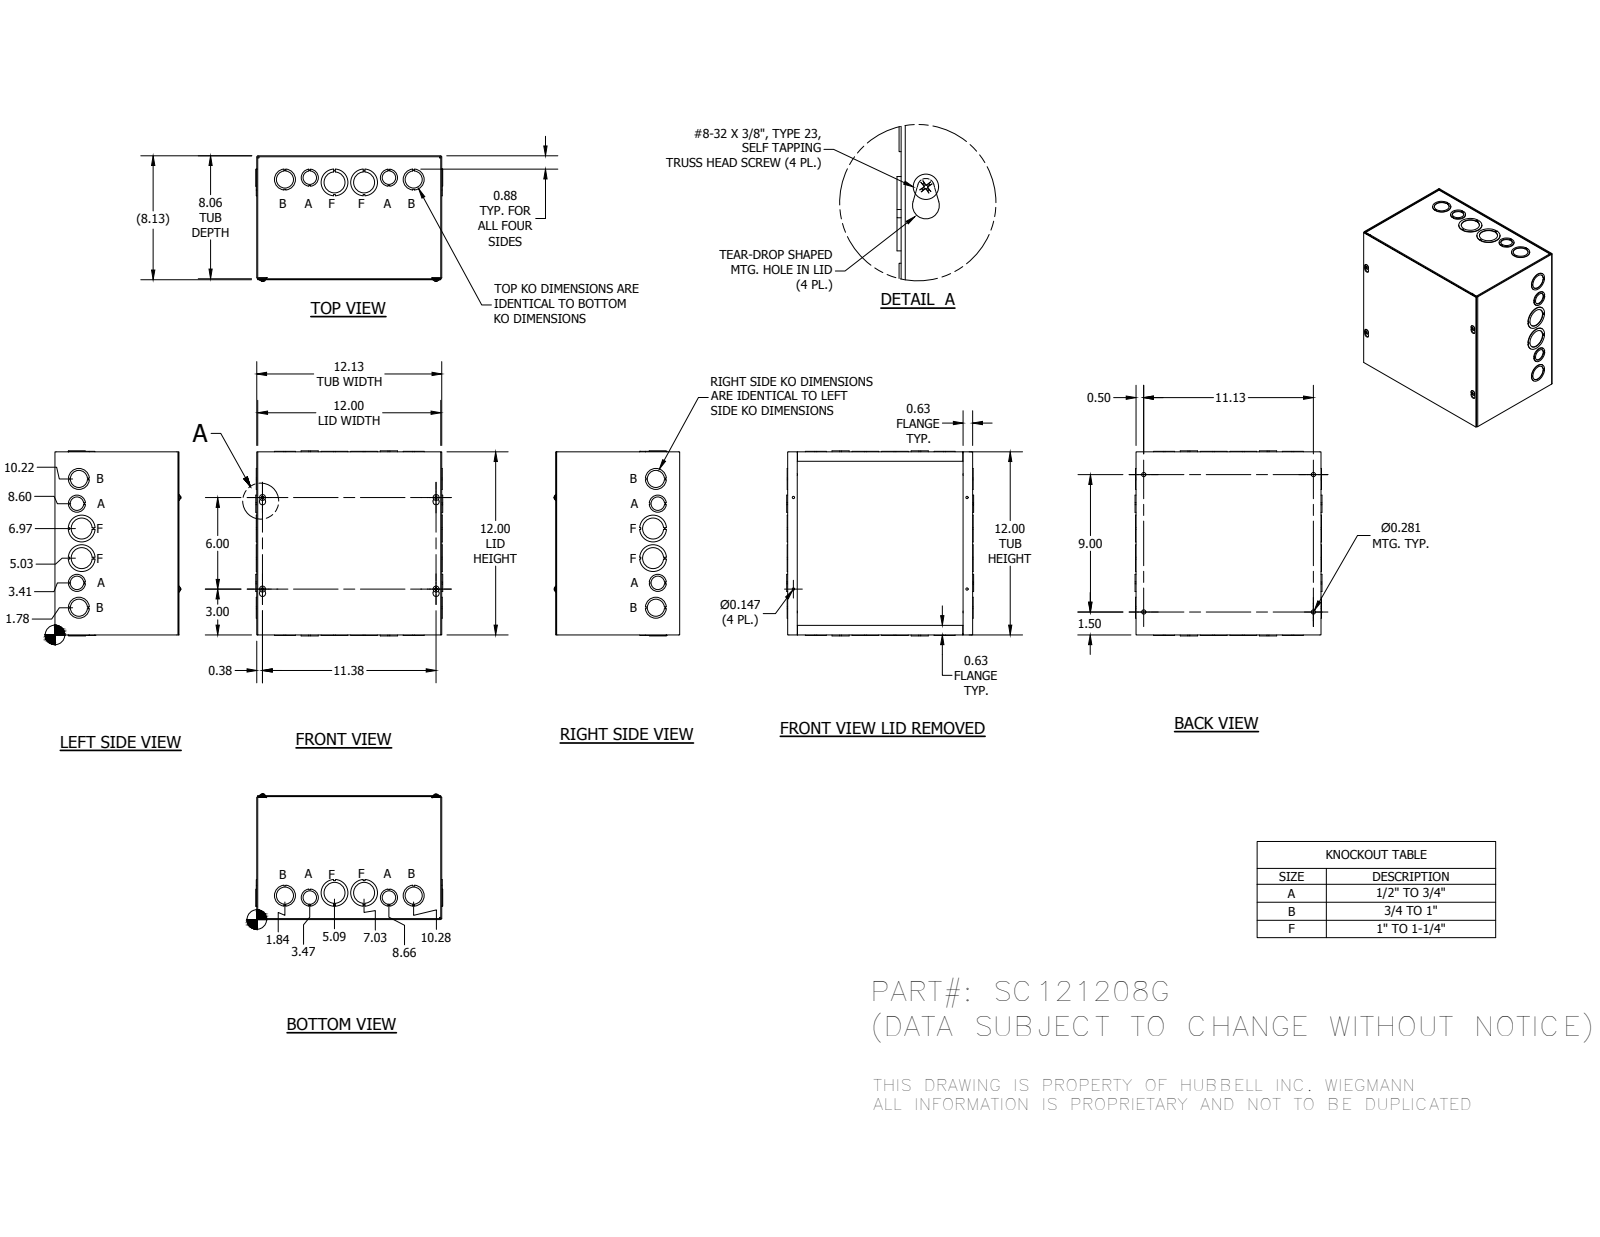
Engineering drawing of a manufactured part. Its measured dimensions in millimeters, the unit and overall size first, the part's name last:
Units: millimetres
Overall size (bounding box): 311.15 × 307.98 × 208.92
Round holes (diameter × count): ⌀28.57 ×8, ⌀34.92 ×8, ⌀3.73 ×4, ⌀7.14 ×4, ⌀22.22 ×4, ⌀44.45 ×4
Round bosses / shafts (diameter × count): ⌀9.75 ×4, ⌀4.17 ×4
Partial cylindrical surfaces — rounded edges, fillets, slot ends (radius × count): R0.4 ×12, R1.98 ×12, R3.17 ×4, R5.16 ×4
Main face-to-face distances: 1.59, 304.8, 303.21, 203.2, 306.39, 1.58, 204.78, 204.79, 206.37, 301.62
Hole centre spacings: 38.23, 41.4, 42.03, 82.69, 90.9, 131.92, 173.13, 190.53
Bodies: 21 solids, 943 faces (683 planar, 192 cylindrical, 68 other)
Part name (STEP PRODUCT): SC121208GBLR; SC1208GTB; SC1212GLPA; 34056 (+1 more)
STEP written by: Autodesk Inventor 2014 (AUTOMOTIVE_DESIGN)
